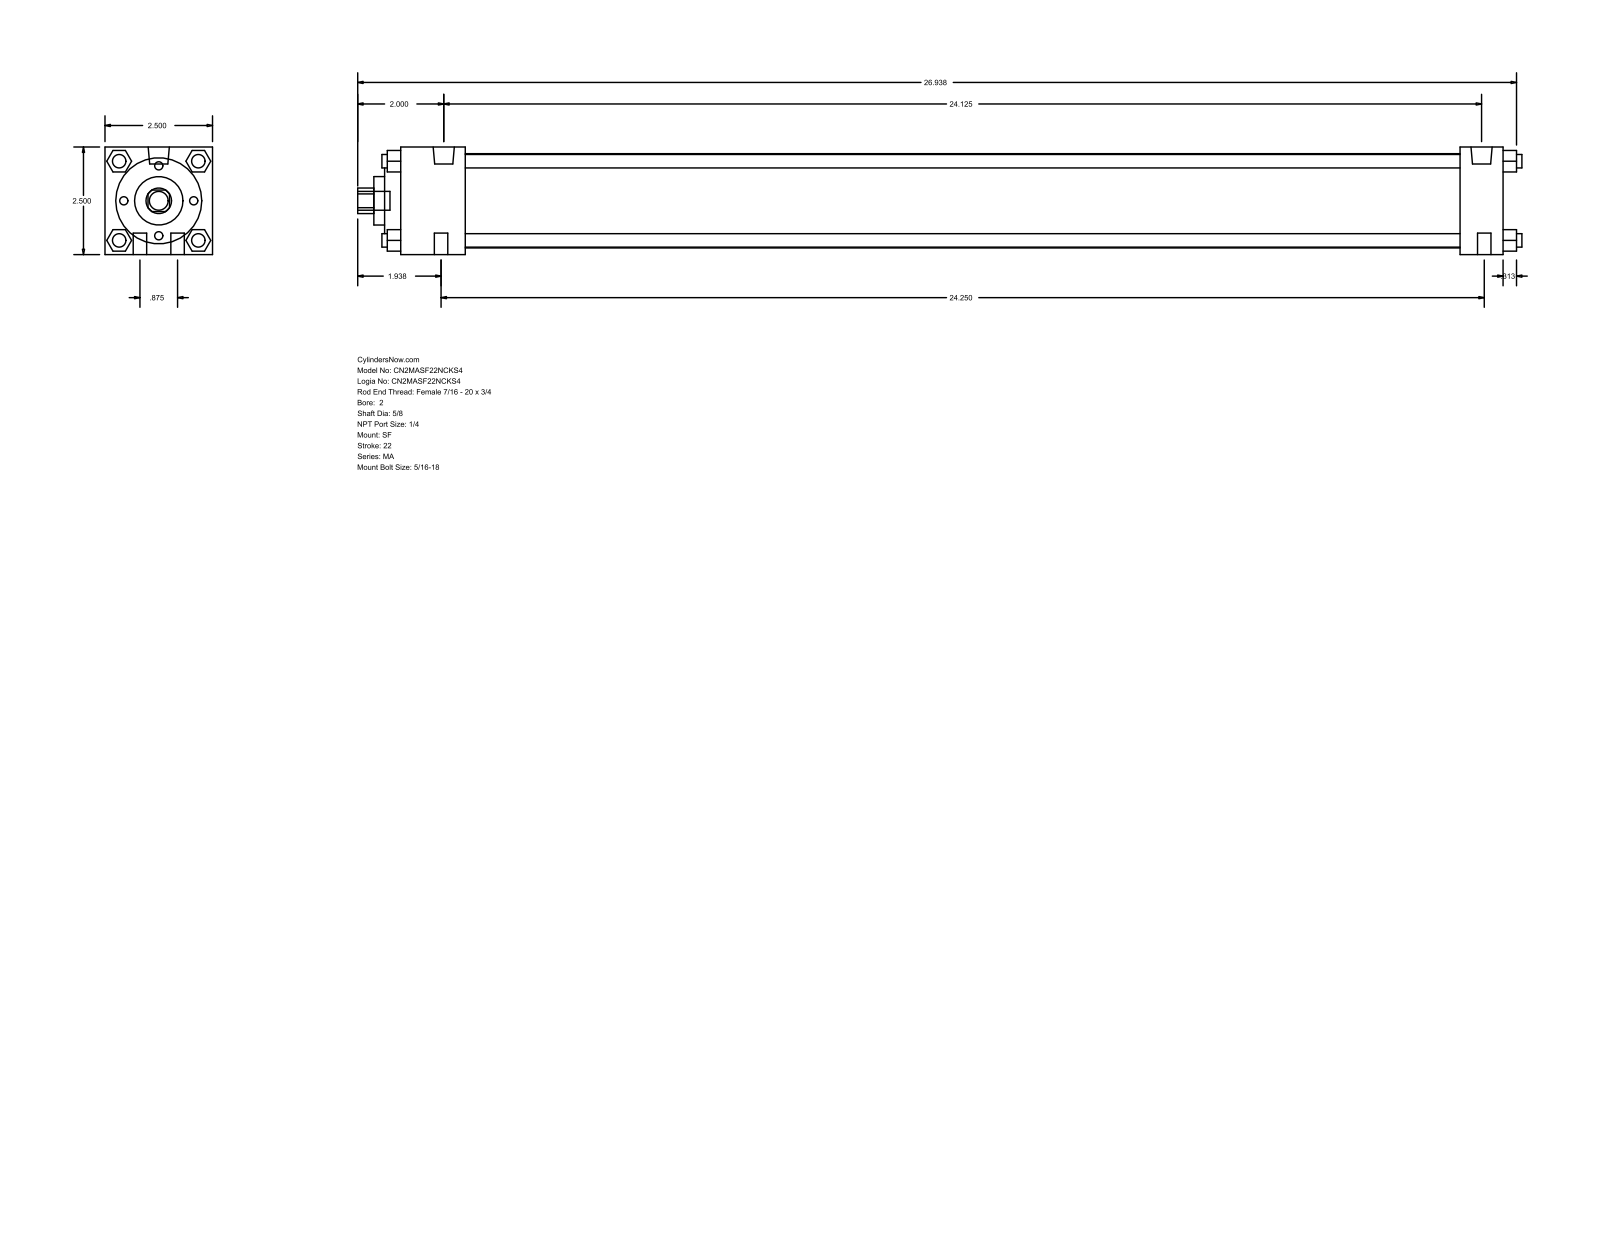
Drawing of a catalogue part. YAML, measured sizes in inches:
part_name: "MA_SF__0200_0.625"
step_written_by: "GSSL Pune (CONFIG_CONTROL_DESIGN)"
units: inches
bodies: {solids: 0, faces: 126, planar: 95, cylindrical: 31, other: 0}
overall_size: [27.063, 2.5, 2.5]
round_holes:
  - {diameter: 0.625, count: 1}
  - {diameter: 1.125, count: 1}
  - {diameter: 2, count: 1}
  - {diameter: 2.19, count: 1}
round_bosses_or_shafts:
  - {diameter: 0.313, count: 10}
  - {diameter: 0.492, count: 2}
  - {diameter: 0.437, count: 1}
partial_cylinders:
  - {radius: 0.297, count: 1}
face_to_face_distances: [2.5, 0.5, 1.5, 0.375, 25.625, 24.625, 1, 23.125, 24.125, 1.875]
